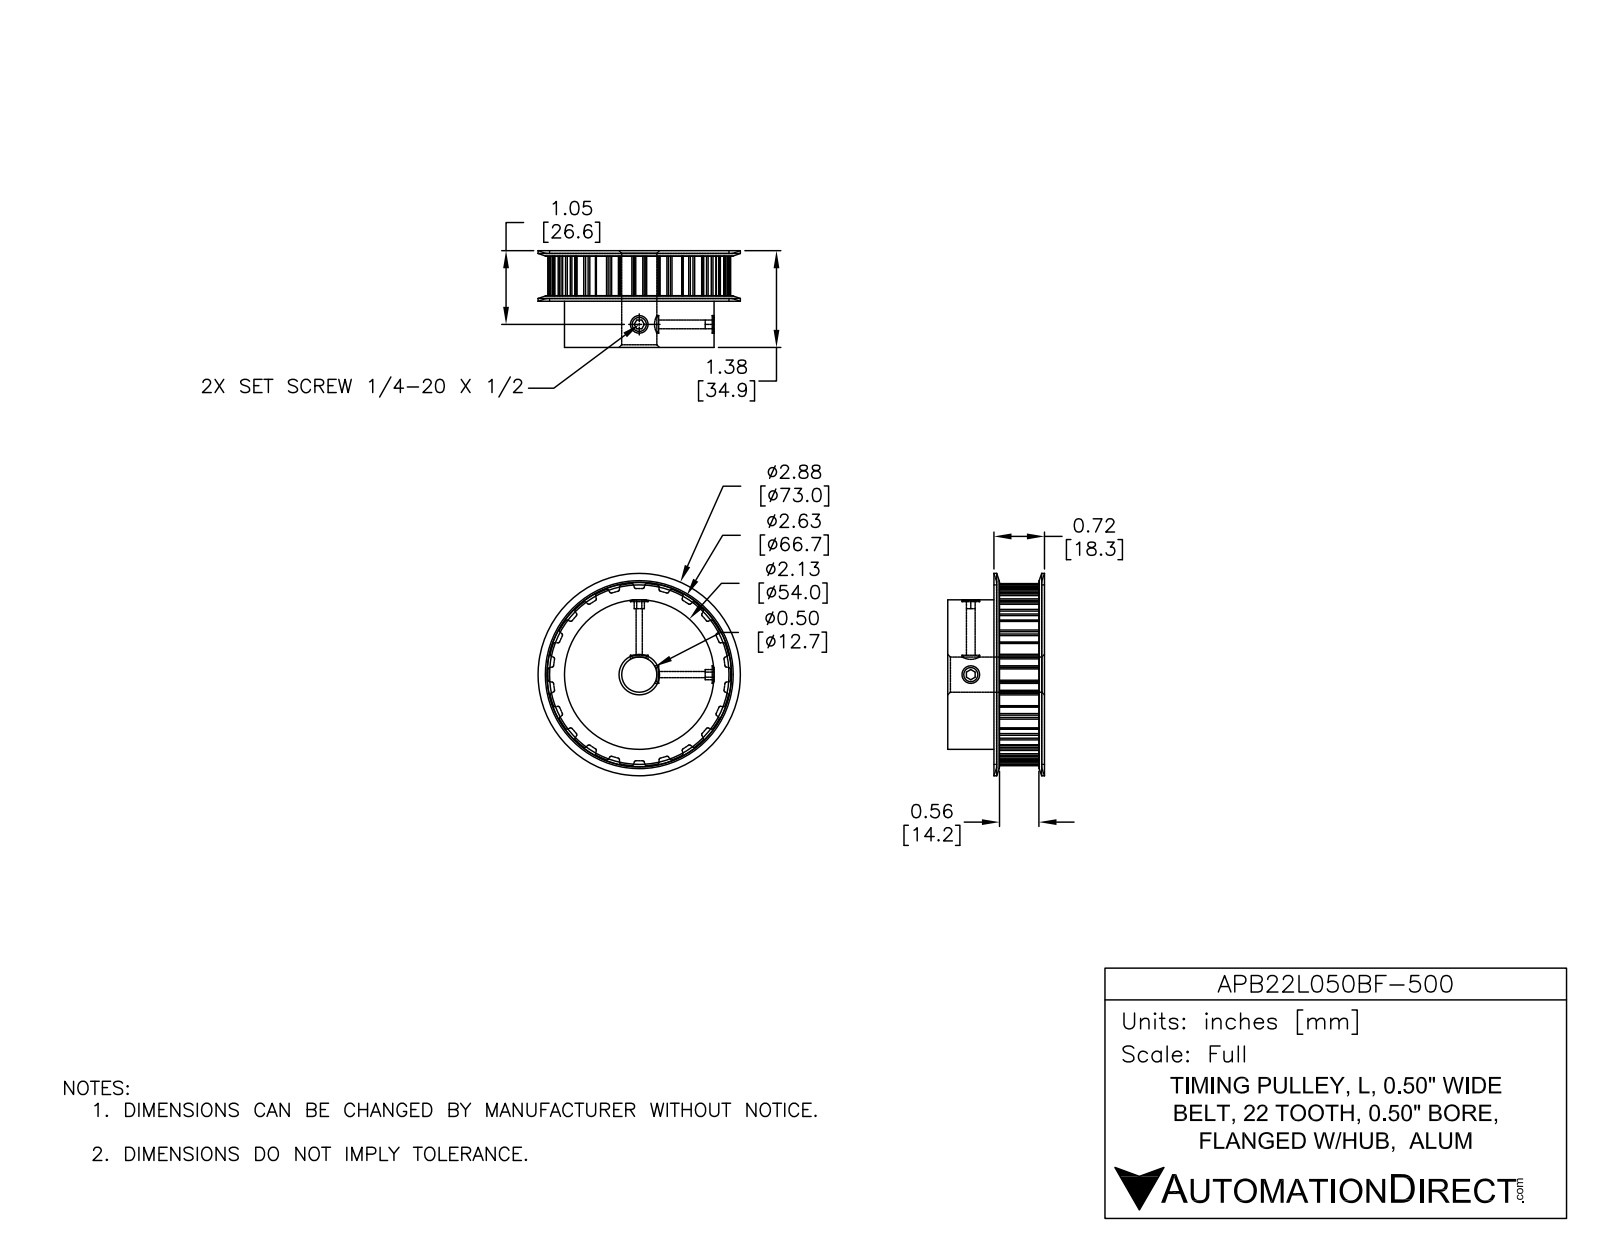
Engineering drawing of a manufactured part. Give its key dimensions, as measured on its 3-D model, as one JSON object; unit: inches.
{"part_name": "APB22L050BF-500", "step_written_by": "SolidWorks 2014 (AUTOMOTIVE_DESIGN)", "units": "inches", "bodies": {"solids": 1, "faces": 178, "planar": 72, "cylindrical": 84, "other": 22}, "overall_size": [2.875, 2.875, 1.375], "volume_in3": 5.816, "surface_area_in2": 28.73, "round_holes": [[0.088, 2], [0.5, 1]], "round_bosses_or_shafts": [[2.125, 1]], "partial_cylinders_radius": [[0.015, 44], [1.243, 1]], "face_to_face_distances": [1.375, 0.71, 0.665, 0.04, 0.67, 1.335, 2.596, 0.04, 0.63, 1.009]}
